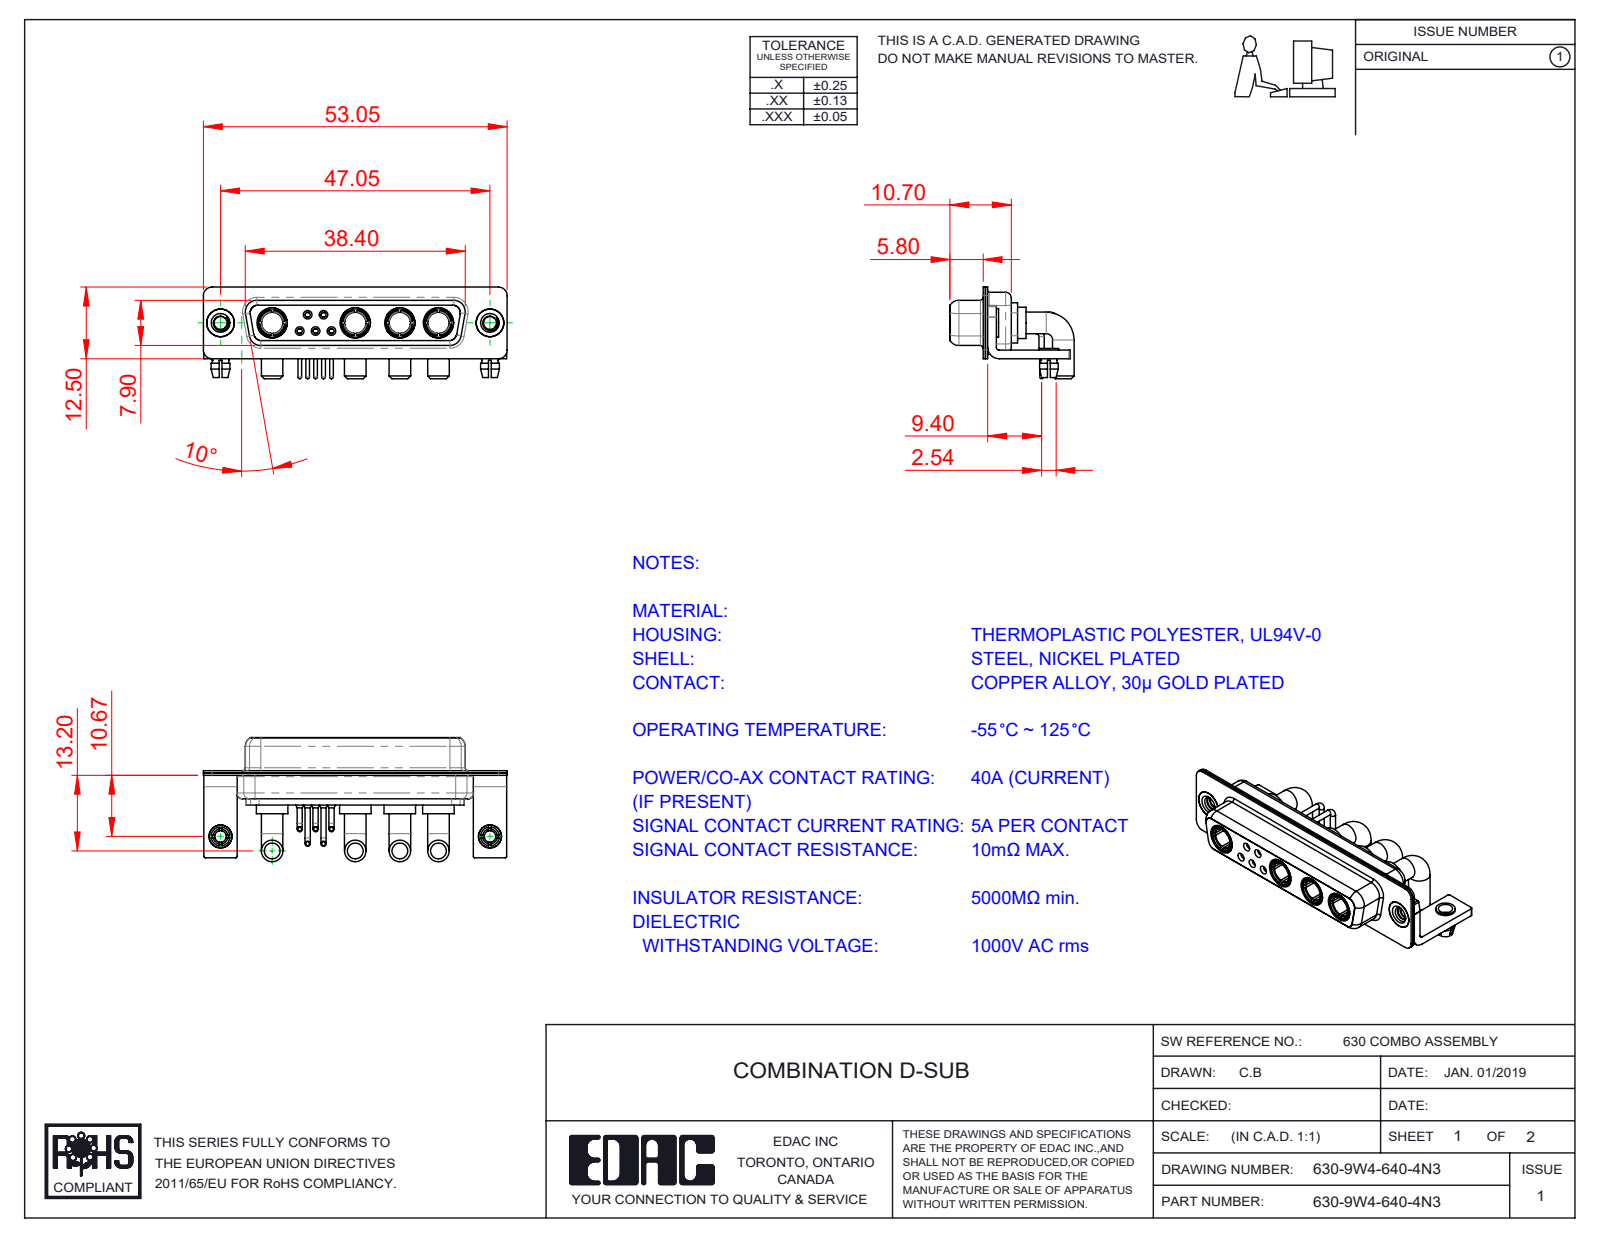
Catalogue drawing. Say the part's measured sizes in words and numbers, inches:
The part is named "630-9W4-640-4N3; 630Combo Housing_9W4; Power Socket_40A RA; 630Combo Board Lock (+6 more)". Its 3-D file was written by "SolidWorks 2020 (CONFIG_CONTROL_DESIGN)". It is 22 solids with 988 faces: 326 planar, 402 cylindrical and 260 other. Overall it measures 2.089 by 0.854 by 0.63 inches. Its volume is 0.282 cubic inches and its surface area 15.22 square inches. Round holes: 7 of diameter 0.079, 6 of diameter 0.191, 5 of diameter 0.035, 5 of diameter 0.043, 5 of diameter 0.059, 4 of diameter 0.146, 4 of diameter 0.209, 3 of diameter 0.063, 2 of diameter 0.067, 2 of diameter 0.089, 2 of diameter 0.098, 2 of diameter 0.126. Round bosses or shafts: 8 of diameter 0.148, 5 of diameter 0.035, 5 of diameter 0.026, 4 of diameter 0.217, 4 of diameter 0.205, 4 of diameter 0.195, 4 of diameter 0.187, 2 of diameter 0.197. Partial cylindrical surfaces (rounded edges, fillets, slot ends): 16 of radius 0.01, 16 of radius 0.059, 13 of radius 0.079, 8 of radius 0.053, 8 of radius 0.063, 5 of radius 0.02, 4 of radius 0.024, 4 of radius 0.026. The main face-to-face distances are 0.016, 0.018, 0.055, 0.333, 0.071, 0.031, 0.35, 0.244, 0.059, 0.278. The hole center spacings are 0.124, 0.109, 1.852, 0.173, 0.198, 0.198, 0.198, 0.218.
